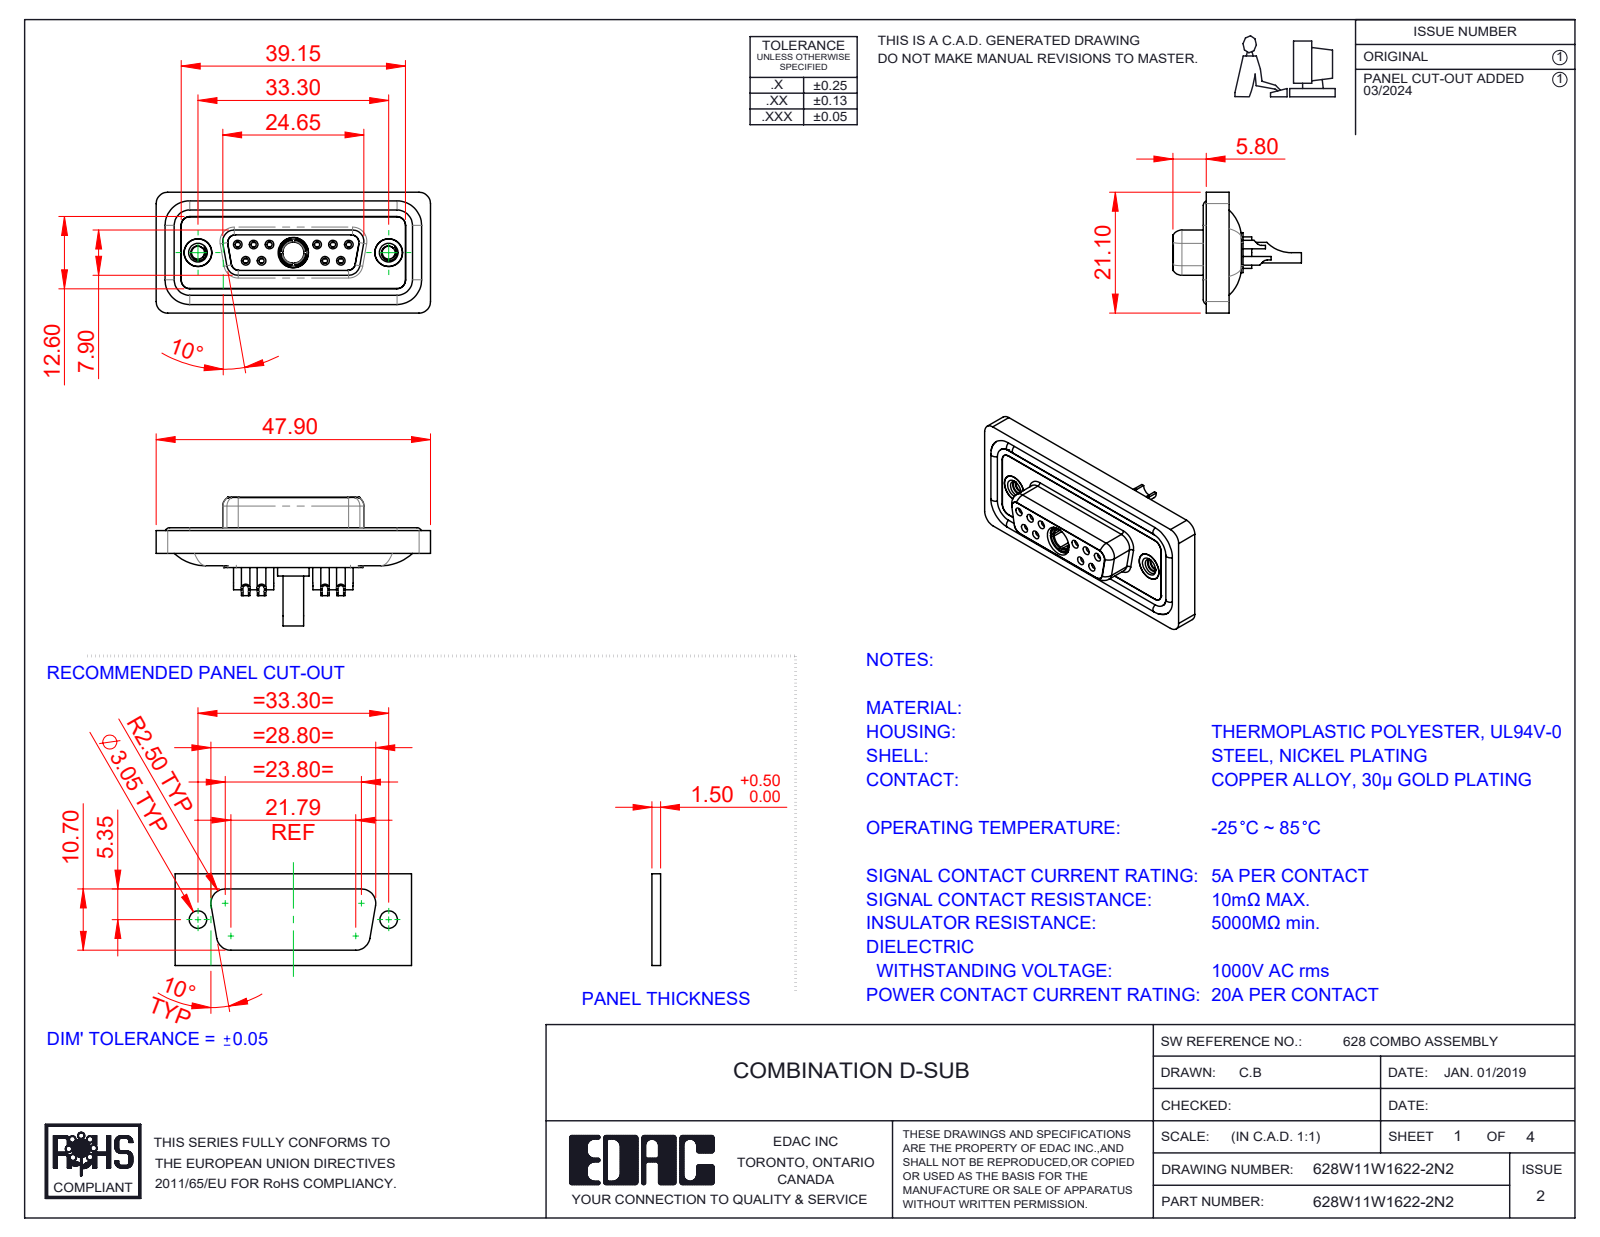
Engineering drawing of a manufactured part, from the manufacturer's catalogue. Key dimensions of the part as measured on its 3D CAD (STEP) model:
Part name (STEP PRODUCT): 628Combo Shell Rear_15 Contacts; 628Combo Threaded Rivet_2; 628Combo Waterproof Housing_15 Contacts; 628Combo Contact Row 1_22 (+5 more)
STEP written by: SolidWorks 2023 (CONFIG_CONTROL_DESIGN)
Units: millimetres
Bodies: 19 solids, 1016 faces (307 planar, 424 cylindrical, 285 other)
Overall size (bounding box): 47.9 × 22.45 × 21.1
Volume: 6 158 mm³ · Surface area: 10 215 mm²
Round holes (diameter × count): ⌀0.9 ×10, ⌀1 ×10, ⌀1.1 ×10, ⌀1.5 ×10, ⌀2 ×10, ⌀1.7 ×6, ⌀1.6 ×4, ⌀4.85 ×3, ⌀2.26 ×2, ⌀4 ×2, ⌀4.05 ×2, ⌀5 ×2
Round bosses / shafts (diameter × count): ⌀2.2 ×10, ⌀1.6 ×10, ⌀4.95 ×2, ⌀4.8 ×2, ⌀5.5 ×1, ⌀5.2 ×1, ⌀4.96 ×1, ⌀4.75 ×1
Partial cylindrical surfaces — rounded edges, fillets, slot ends (radius × count): R1.5 ×22, R2 ×20, R1.35 ×12, R1.6 ×8, R1 ×6, R0.25 ×4, R0.5 ×4, R0.6 ×4
Main face-to-face distances: 0.4, 1.6, 1.8, 2.9, 0.5, 1.1, 5.65, 7.45, 6.6, 7.05
Hole centre spacings: 3.16, 2.77, 13.85, 11.08, 16.62, 5.03, 5.04, 5.54
